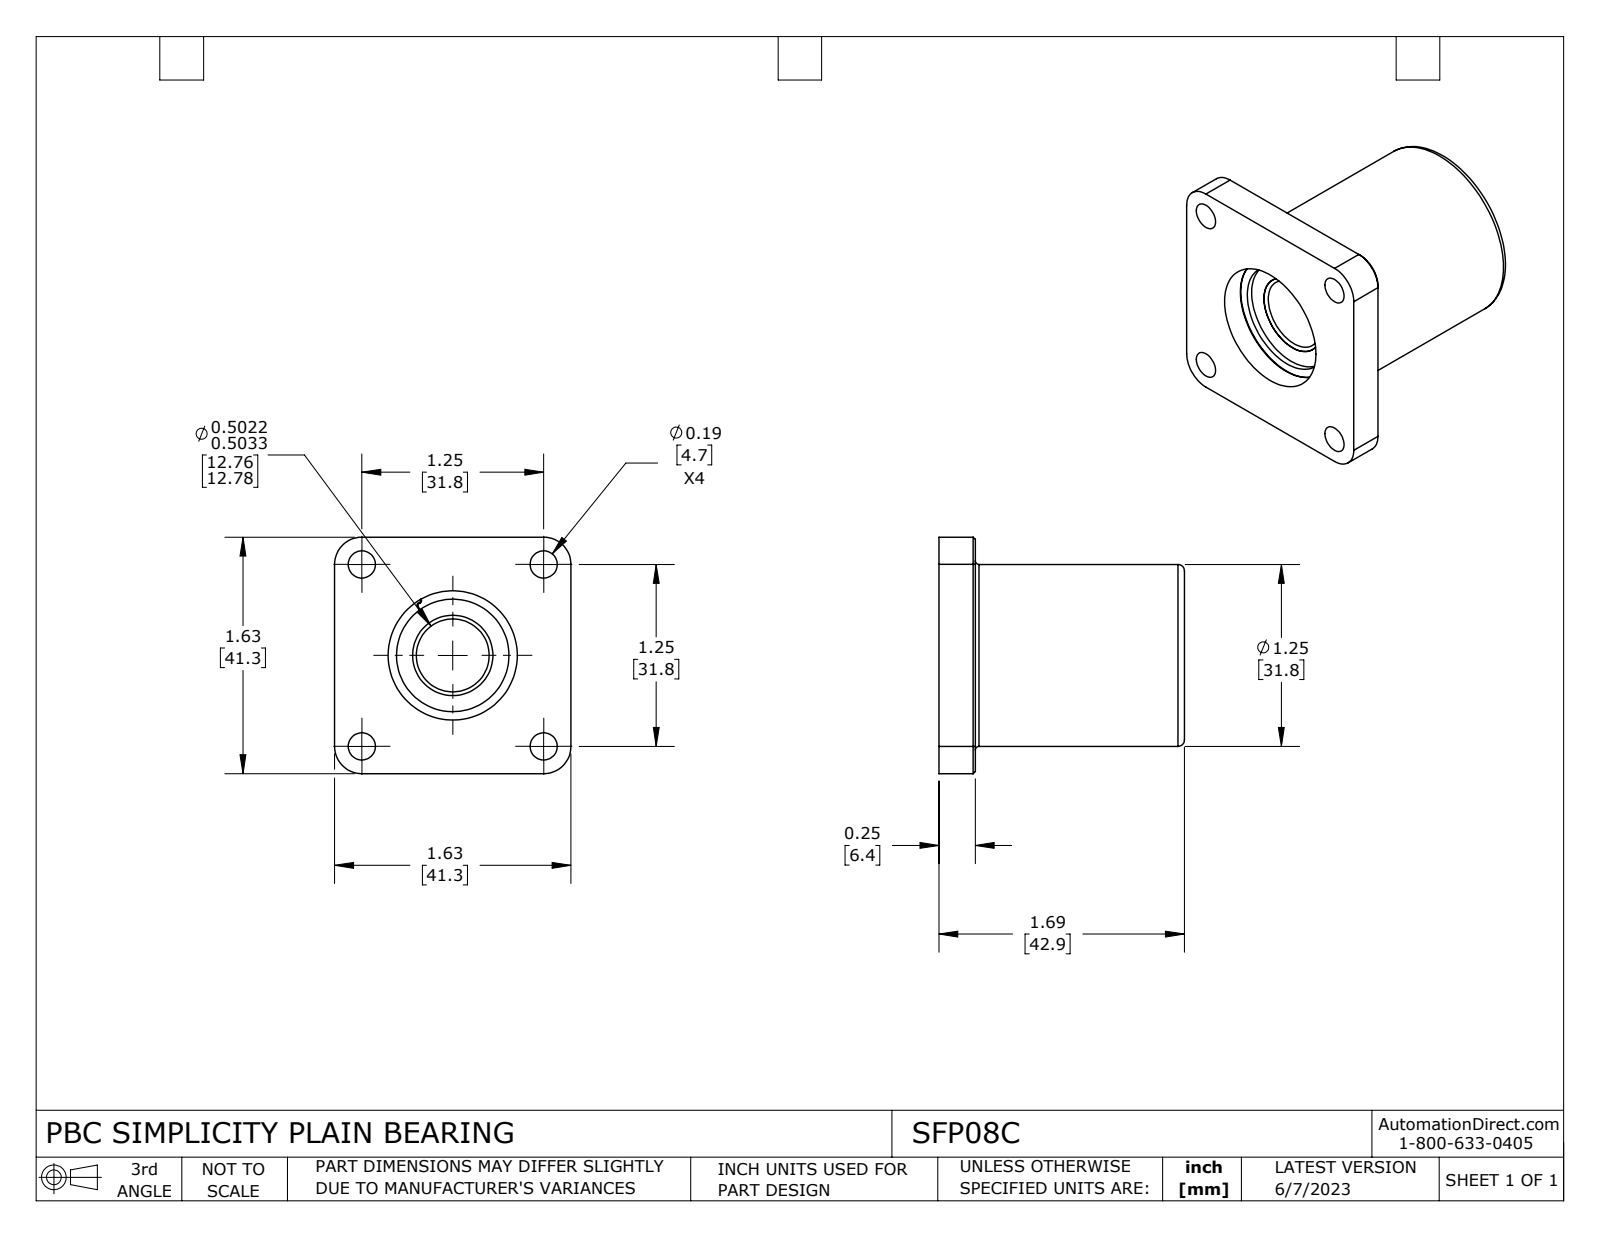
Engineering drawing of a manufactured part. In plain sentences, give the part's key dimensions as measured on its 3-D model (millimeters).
The part is named "SFP08C". Its 3-D file was written by "SolidWorks 2021 (CONFIG_CONTROL_DESIGN)". It is 7 solids with 169 faces: 41 planar, 74 cylindrical and 54 other. Overall it measures 42.9 by 41.3 by 41.3 millimeters. Its volume is 30 230 cubic millimeters and its surface area 19 700 square millimeters. Round holes: 4 of diameter 4.7, 1 of diameter 12.7, 1 of diameter 14, 1 of diameter 19.6, 1 of diameter 22.6, 1 of diameter 23.6. Round bosses or shafts: 1 of diameter 31.8, 1 of diameter 24, 1 of diameter 22.2, 1 of diameter 20.8, 1 of diameter 18.1. Partial cylindrical surfaces (rounded edges, fillets, slot ends): 4 of radius 0.4, 4 of radius 4.7, 2 of radius 0.2, 2 of radius 0.5. The main face-to-face distances are 6.4, 41.3, 4.2, 38.7, 42.9, 36.5, 9.4, 12.6, 19, 22.2. The hole center spacings are 22.5, 31.8, 44.9.
